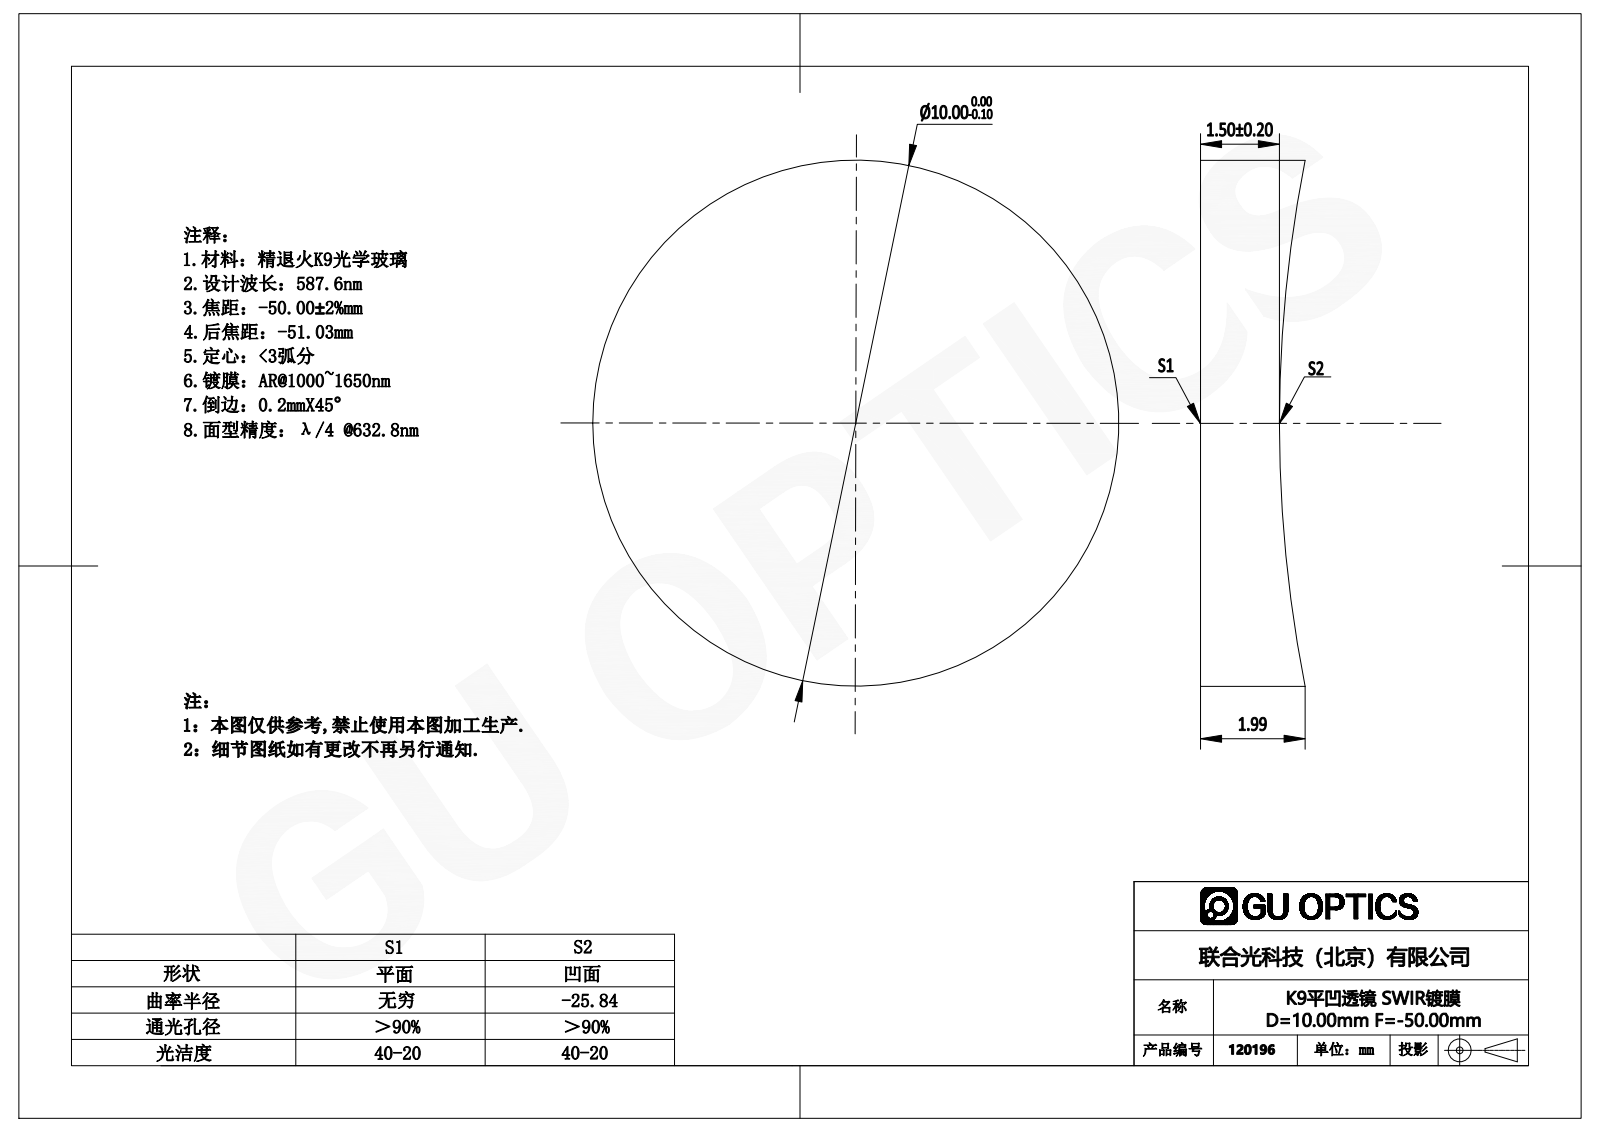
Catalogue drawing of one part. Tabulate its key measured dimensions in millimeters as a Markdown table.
| quantity | value |
| --- | --- |
| part name | 120136 |
| STEP written by | SolidWorks 2016 (AUTOMOTIVE_DESIGN) |
| units | millimeters |
| bodies | 1 solid, 5 faces (1 planar, 2 cylindrical, 2 other) |
| overall size | 10 × 10 × 1.99 |
| volume | 137 mm³ |
| surface area | 220 mm² |
| round bosses / shafts (diameter × count) | 10 × 1 |
